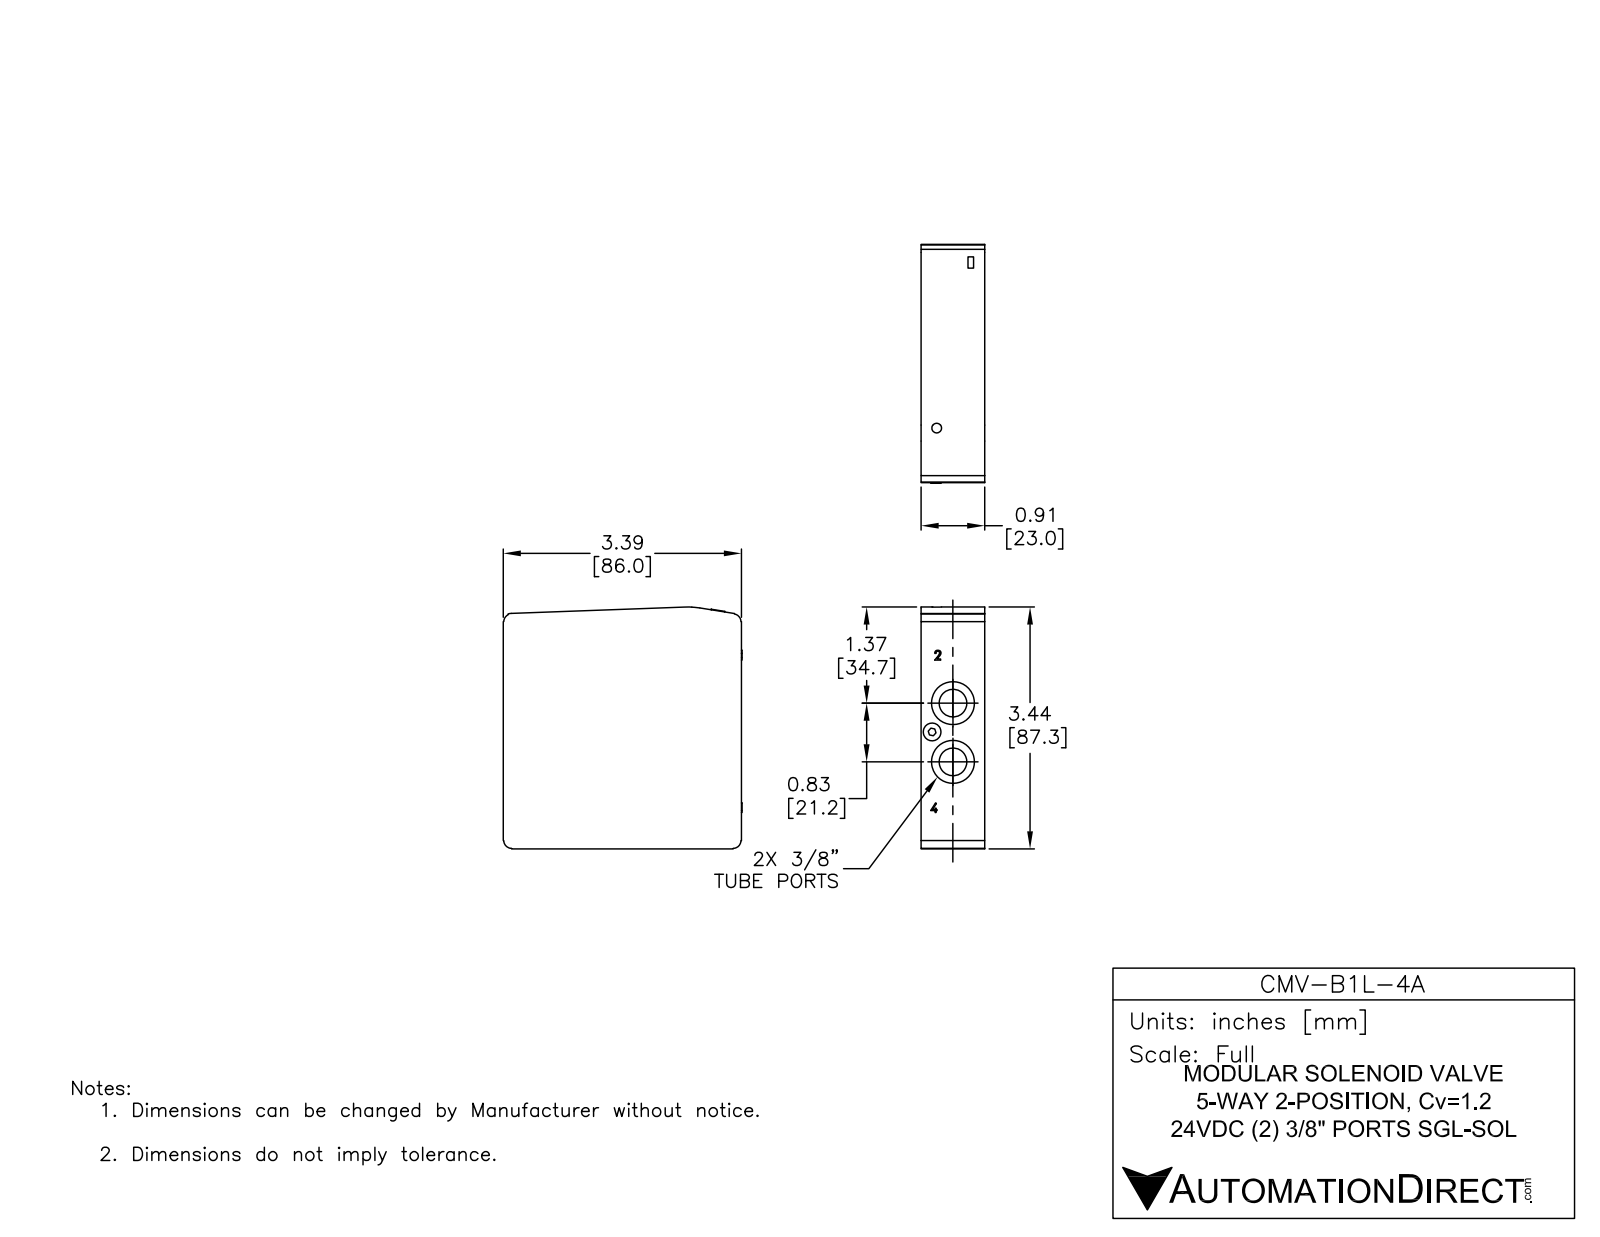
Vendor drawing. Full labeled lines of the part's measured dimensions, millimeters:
Part name (STEP PRODUCT): CMV-B1L-4A
STEP written by: SolidWorks 2013 (AUTOMOTIVE_DESIGN)
Units: millimetres
Bodies: 74 solids, 1145 faces (889 planar, 159 cylindrical, 97 other)
Overall size (bounding box): 89.5 × 87.3 × 31.43
Volume: 154 043 mm³ · Surface area: 54 266 mm²
Round holes (diameter × count): ⌀4.4 ×4, ⌀5.25 ×4, ⌀6.5 ×2, ⌀9.75 ×2, ⌀14 ×2, ⌀18 ×2, ⌀3.35 ×1, ⌀3.6 ×1, ⌀6.25 ×1, ⌀6.4 ×1
Round bosses / shafts (diameter × count): ⌀4 ×4, ⌀1.5 ×4, ⌀15.25 ×2, ⌀11 ×2, ⌀6.25 ×2, ⌀5.75 ×2, ⌀4.2 ×2, ⌀3.5 ×1
Partial cylindrical surfaces — rounded edges, fillets, slot ends (radius × count): R2.35 ×12, R0.78 ×4, R1.5 ×4, R2.8 ×4, R0.15 ×2, R0.25 ×2, R1 ×2, R0.17 ×1
Main face-to-face distances: 22.5, 12.5, 10, 83, 3, 1, 65.12, 50.25, 32.75, 53.25
Hole centre spacings: 9.7, 11.99, 12.17, 16, 22.17, 31.45, 31.52, 39.5
